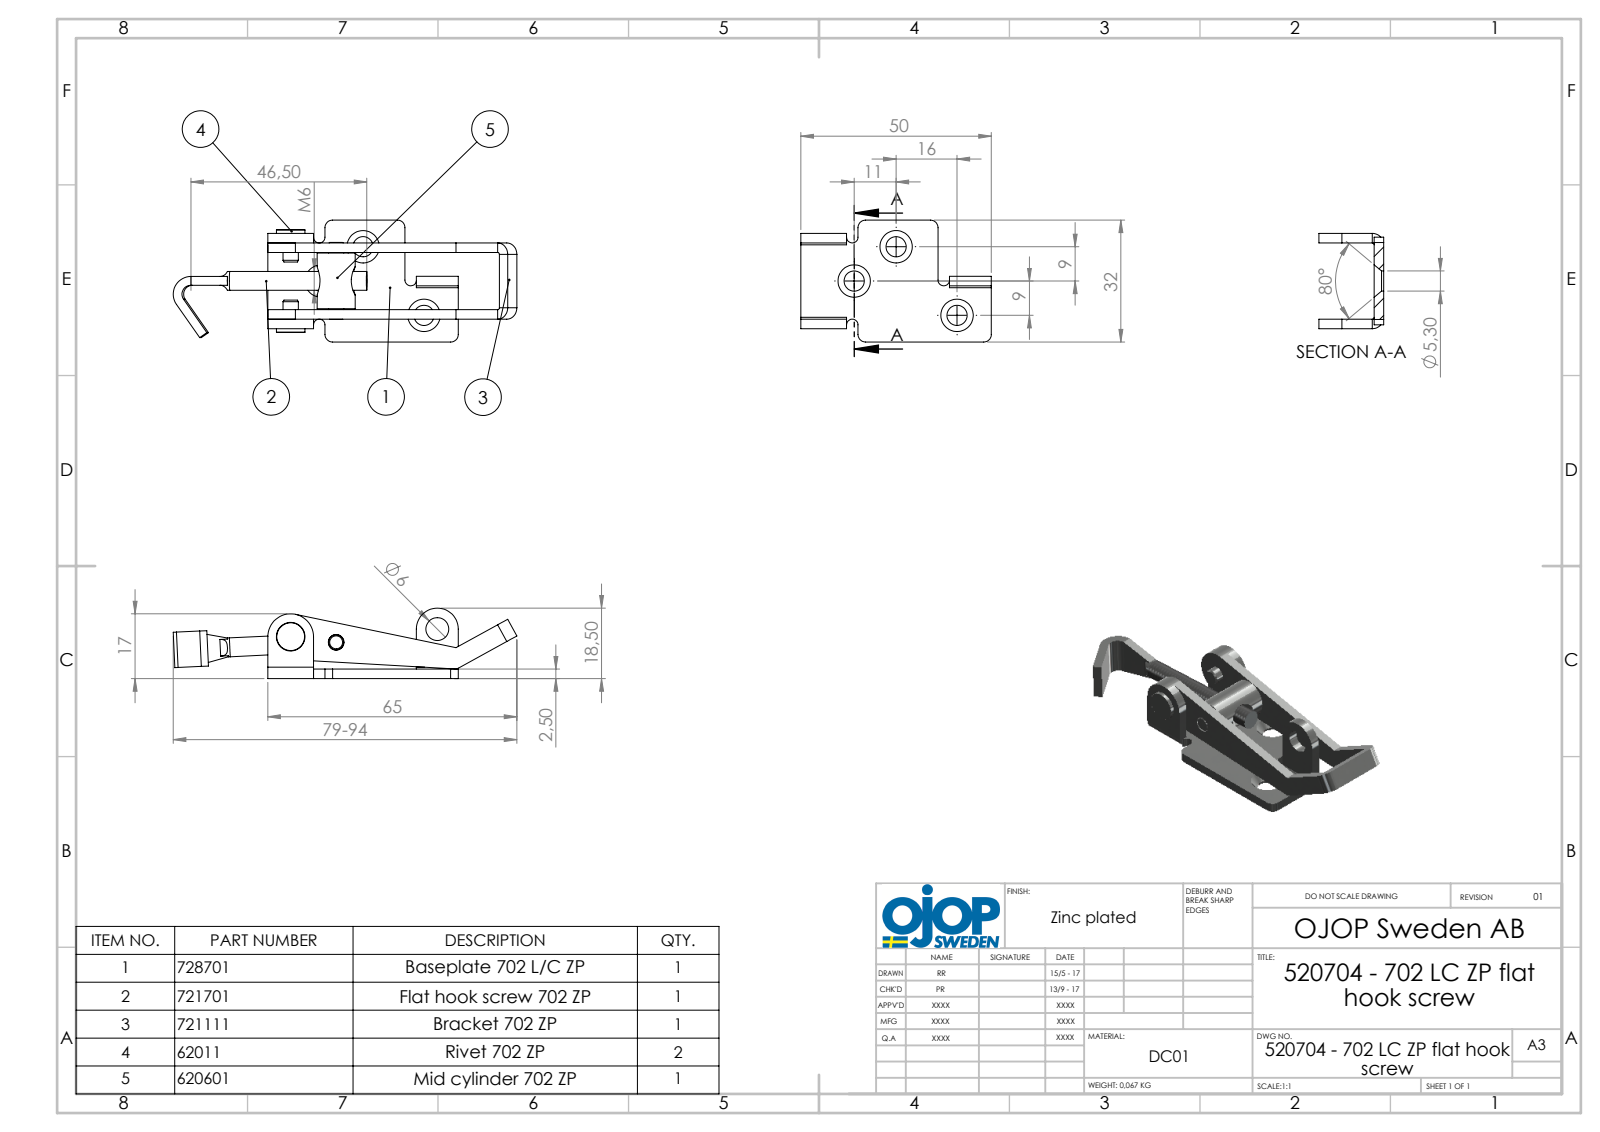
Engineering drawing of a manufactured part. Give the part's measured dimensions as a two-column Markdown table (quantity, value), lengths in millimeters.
| quantity | value |
| --- | --- |
| part name | 702 - Bygel; 702 - platthake; 702 - Platta LC; 520704 - HLC fzb (+2 more) |
| STEP written by | SolidWorks 2015 (AUTOMOTIVE_DESIGN) |
| units | millimeters |
| bodies | 6 solids, 171 faces (77 planar, 72 cylindrical, 22 other) |
| overall size | 91.56 × 32 × 18.5 |
| volume | 9 125 mm³ |
| surface area | 9 455 mm² |
| round holes (diameter × count) | 5.3 × 3, 4.1 × 2, 6 × 2, 5 × 1 |
| round bosses / shafts (diameter × count) | 4 × 2, 10 × 1, 7.5 × 1, 4.96 × 1, 4.95 × 1 |
| partial cylindrical surfaces (radius × count) | 2 × 6, 0.5 × 5, 3 × 5, 1.5 × 2, 1.51 × 1, 2.35 × 1, 4.65 × 1, 5.5 × 1 |
| main face-to-face distances | 2.5, 17.5, 20, 8.75, 11.25, 15, 5, 6.25, 22.5, 6 |
| hole center spacings | 12.02, 14.21, 24.08, 26.8, 28.46, 38.55 |
